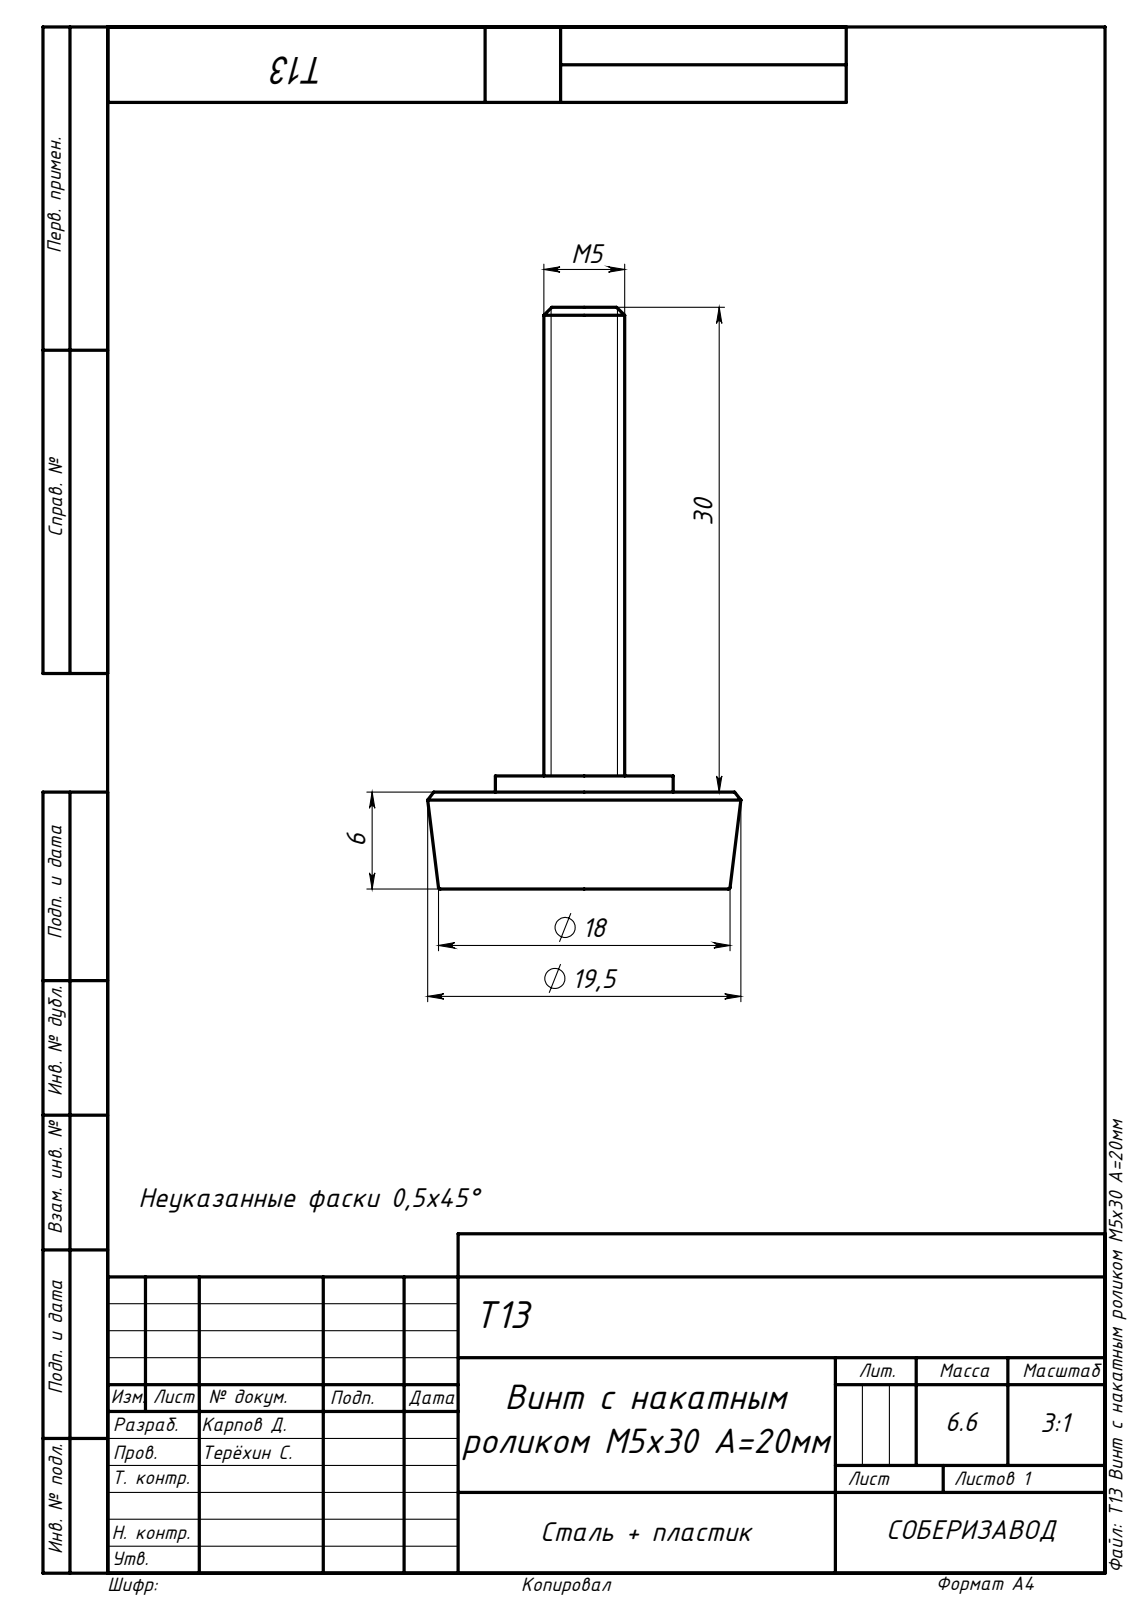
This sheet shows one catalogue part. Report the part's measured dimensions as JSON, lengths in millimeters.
{"part_name": "T13 Винт с накатным роликом М5х30 А=20мм", "step_written_by": "SolidWorks 2021 (AUTOMOTIVE_DESIGN)", "units": "millimeters", "bodies": {"solids": 1, "faces": 19, "planar": 5, "cylindrical": 6, "other": 8}, "overall_size": [36, 19.38, 19.38], "volume_mm3": 2295, "surface_area_mm2": 1411, "round_holes": [[7, 1]], "round_bosses_or_shafts": [[11, 1], [5, 1]], "face_to_face_distances": [6, 7, 1, 36, 30, 29]}
